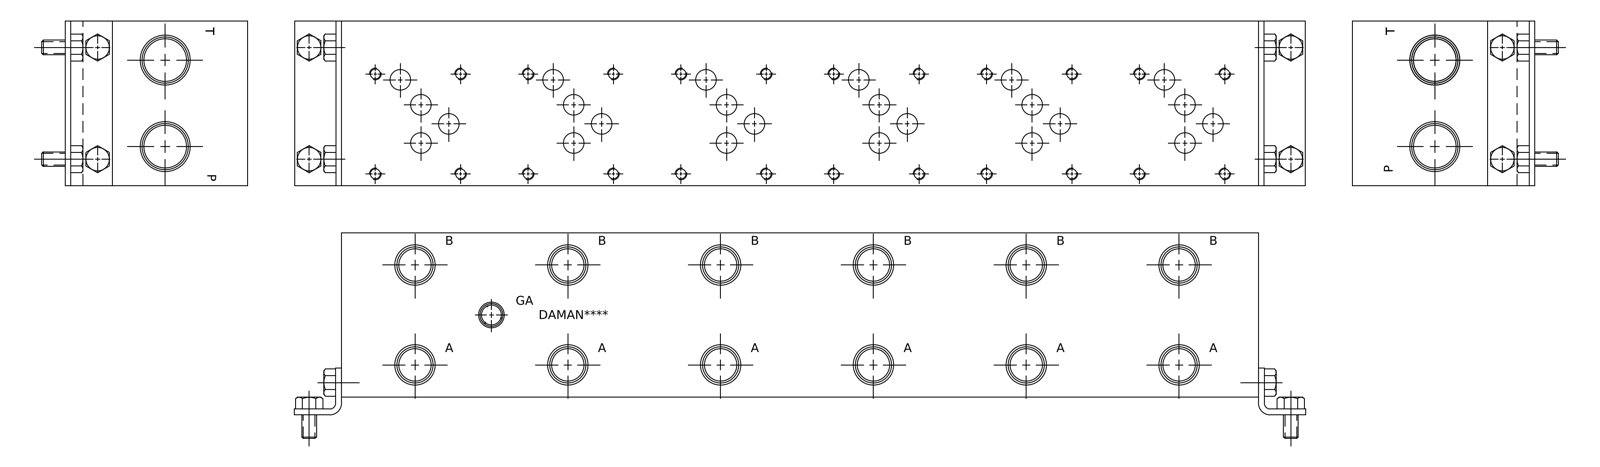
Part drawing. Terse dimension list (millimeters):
name: Part_AD05P063P_3D
written by: Autodesk Inventor 2019 (AUTOMOTIVE_DESIGN)
unit: mm
bodies: 1 solid, 877 faces (473 planar, 114 cylindrical, 290 other)
size: 495.3 × 88.9 × 88.9
volume: 3 768 000 mm³; area: 228 025 mm²
holes: 24× ⌀5.11, 24× ⌀6.35, 24× ⌀11.13, 12× ⌀17.48, 12× ⌀21.59, 2× ⌀6.53, 2× ⌀7.92, 2× ⌀23.01, 2× ⌀26.92, 1× ⌀10.72, 1× ⌀13.87
face distances: 88.9, 495.3, 15.37, 73.53, 15.85, 479.45, 1, 463.6, 14.37, 87.9
hole spacings: 82.55, 165.1, 247.65, 98.61, 330.2, 85.09, 98.17, 173.69
